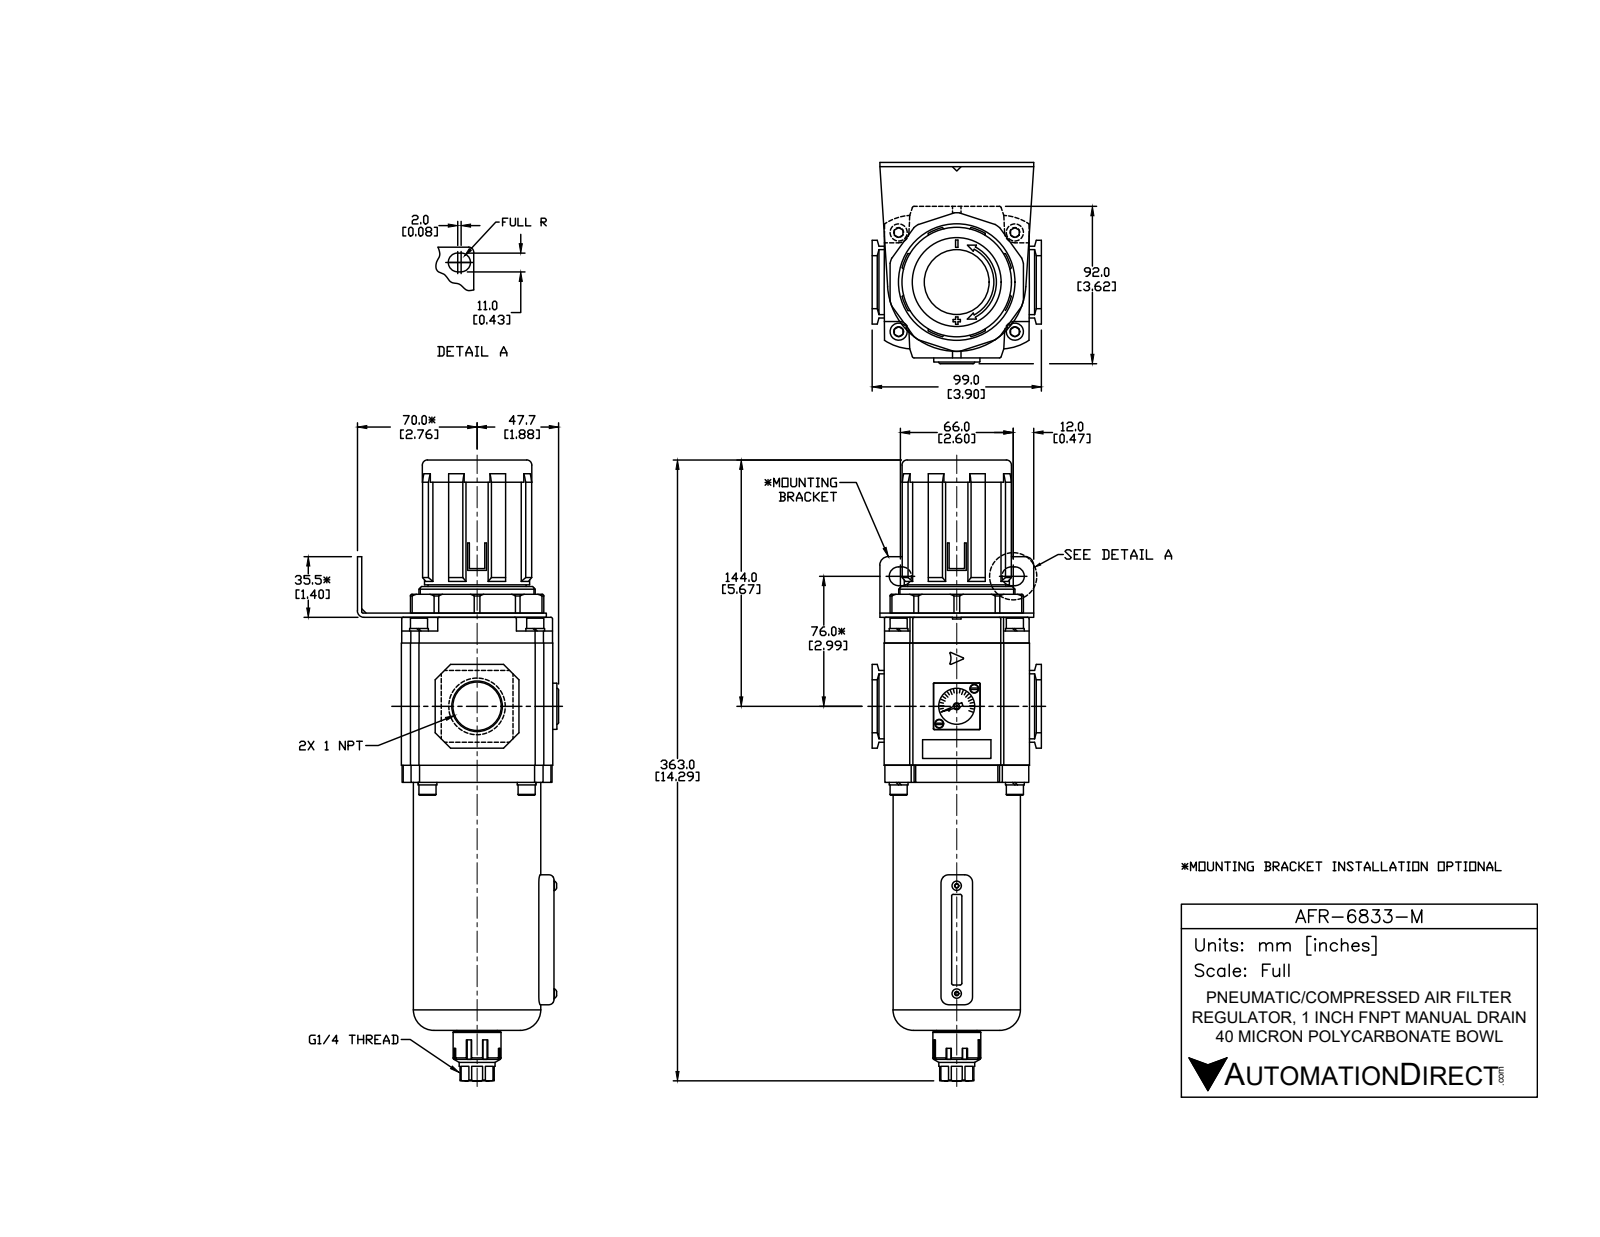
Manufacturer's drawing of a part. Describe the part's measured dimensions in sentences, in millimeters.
The part is named "AFR-6833-M". Its 3-D file was written by "SolidWorks 2015 (CONFIG_CONTROL_DESIGN)". It is 16 solids with 703 faces: 439 planar, 175 cylindrical and 89 other. Overall it measures 362.7 by 117 by 99 millimeters. Its volume is 1 664 000 cubic millimeters and its surface area 186 514 square millimeters. Round holes: 6 of diameter 3, 1 of diameter 2, 1 of diameter 12, 1 of diameter 28.98, 1 of diameter 30, 1 of diameter 38. Round bosses or shafts: 8 of diameter 10, 2 of diameter 5.5, 2 of diameter 2.7, 1 of diameter 68, 1 of diameter 64, 1 of diameter 62, 1 of diameter 53.76, 1 of diameter 28. Partial cylindrical surfaces (rounded edges, fillets, slot ends): 12 of radius 1, 10 of radius 1.2, 8 of radius 1.3, 8 of radius 2.5, 8 of radius 9.5, 8 of radius 19.9, 6 of radius 0.5, 4 of radius 0.3. The main face-to-face distances are 2.5, 91.2, 88.7, 87.6, 1, 88.6, 85, 92, 10, 3.5. The hole center spacings are 41.35, 34.68, 53.16, 63.36, 82.71, 69.35.
